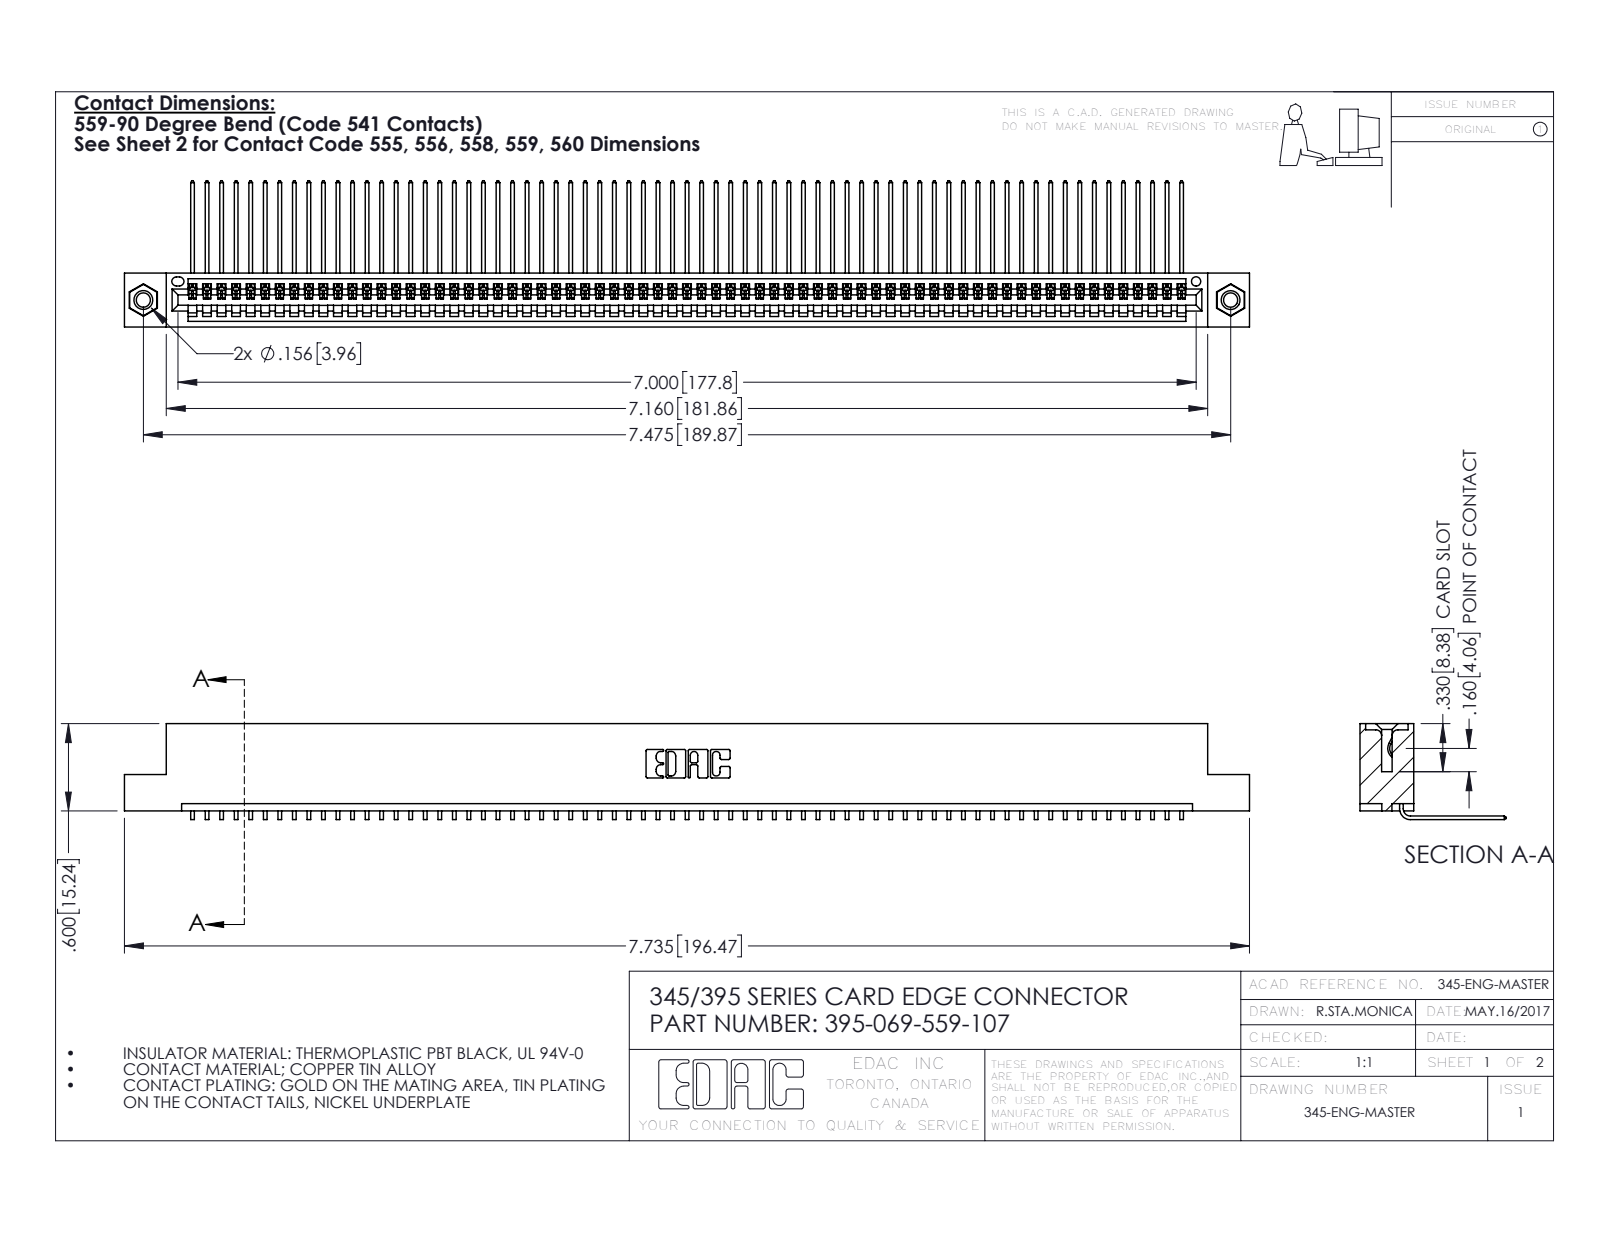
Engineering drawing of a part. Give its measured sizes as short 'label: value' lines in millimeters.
name: 345-250-001_345-250-005-103; 345-292-001_558 559 Tail - 1; 345 Part_Flush Mounting Lugs - 0.156 Dia-TI; 395-069-559-107
written by: SolidWorks 2016 (CONFIG_CONTROL_DESIGN)
unit: mm
bodies: 72 solids, 4326 faces (3010 planar, 1300 cylindrical, 16 other)
size: 196.5 × 25.5 × 16.7
volume: 19 090 mm³; area: 27 130 mm²
holes: 2× ⌀2.5, 2× ⌀3.2, 2× ⌀4, 1× ⌀1.6
bosses: 2× ⌀3.9
rounds: 138× R0.2, 22× R0.3, 6× R0.2, 6× R0.8, 3× R0.7, 2× R0.8, 2× R1, 1× R0.4
face distances: 1.8, 7.6, 9.4, 5.1, 2.5, 6.9, 0.6, 5.7, 3.8, 1.8
hole spacings: 6.9, 183.9, 189.9
